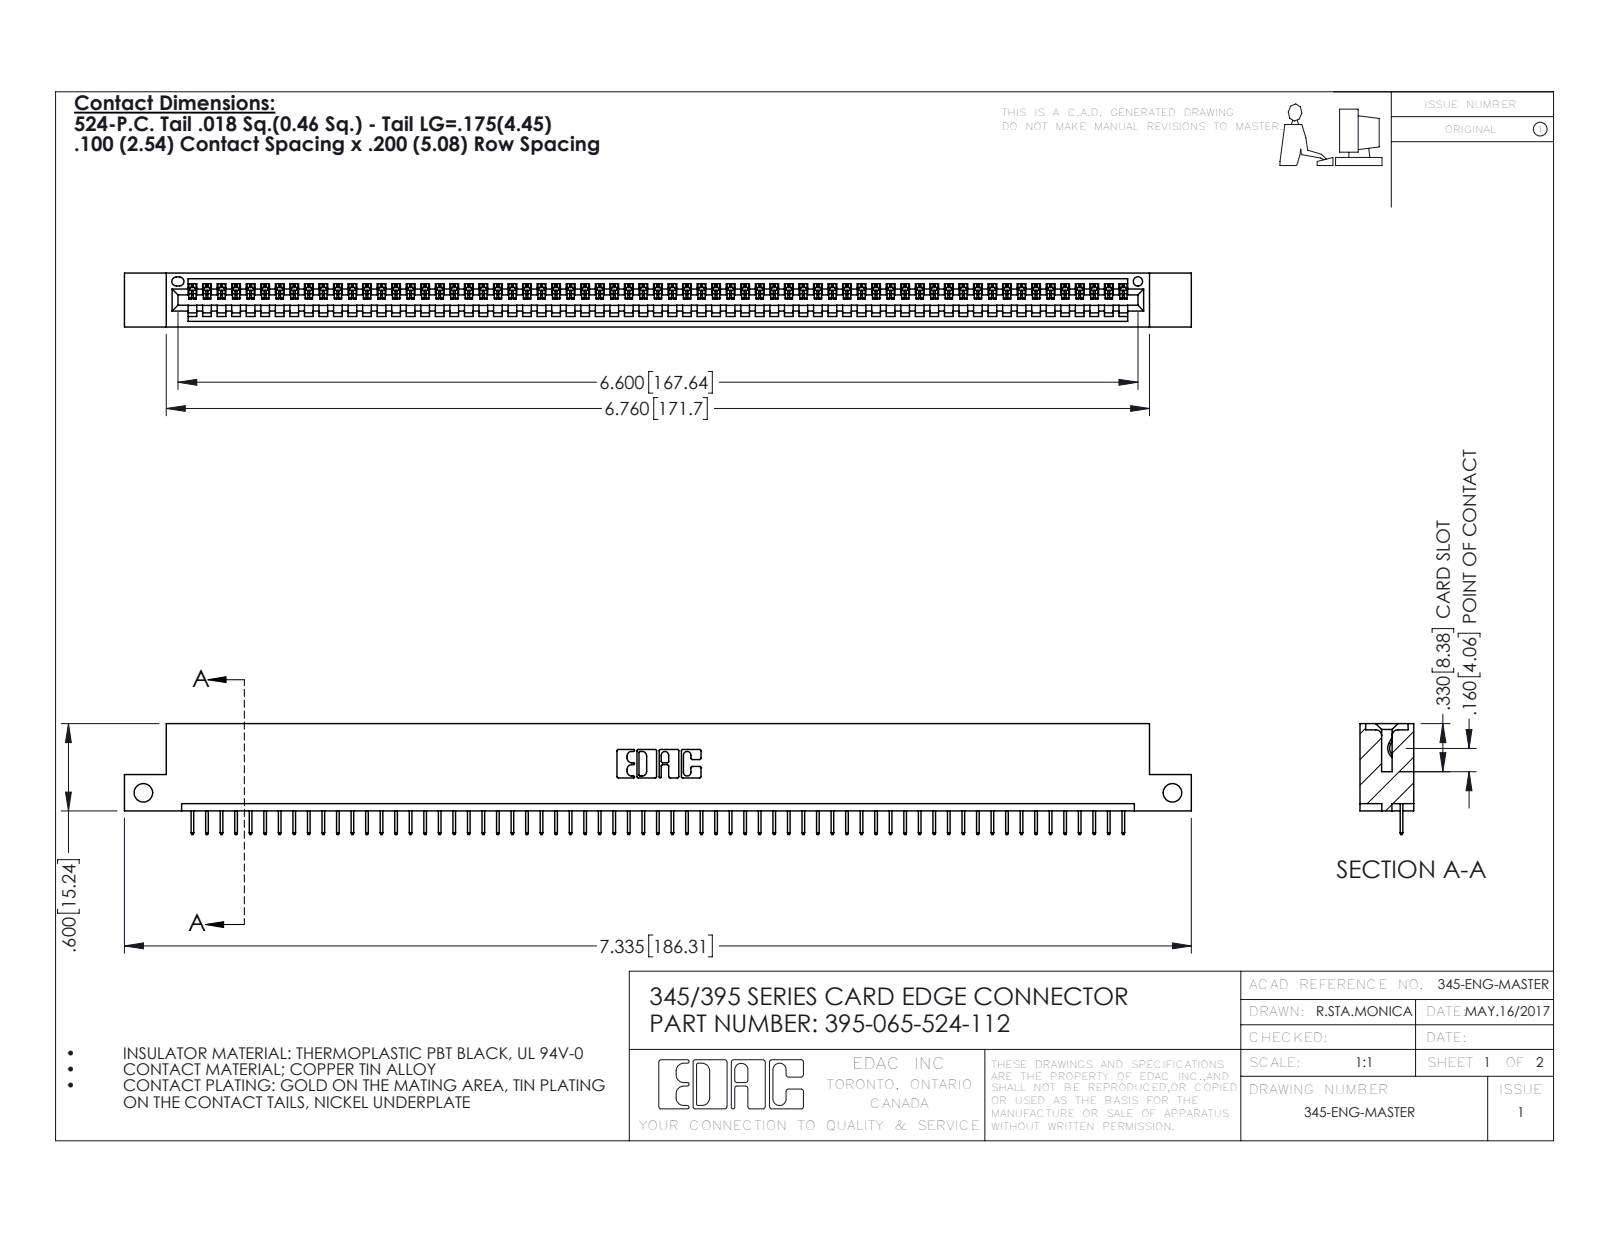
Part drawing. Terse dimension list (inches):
name: 345 Part_Flush Mounting Lugs - Side Mount; 395-065-524-112; 345-292-001_345-293-124
written by: SolidWorks 2016 (CONFIG_CONTROL_DESIGN)
unit: in
bodies: 66 solids, 4156 faces (3070 planar, 1086 cylindrical, 0 other)
size: 7.335 × 0.762 × 0.37
volume: 1.07 in³; area: 35.12 in²
holes: 2× ⌀0.128, 1× ⌀0.064
rounds: 130× R0.006, 22× R0.01, 6× R0.007, 6× R0.031, 3× R0.026, 2× R0.031, 2× R0.04, 1× R0.014
face distances: 0.298, 0.072, 0.37, 0.2, 0.098, 0.272, 0.025, 0.225, 0.072, 0.149
hole spacings: 7.075
